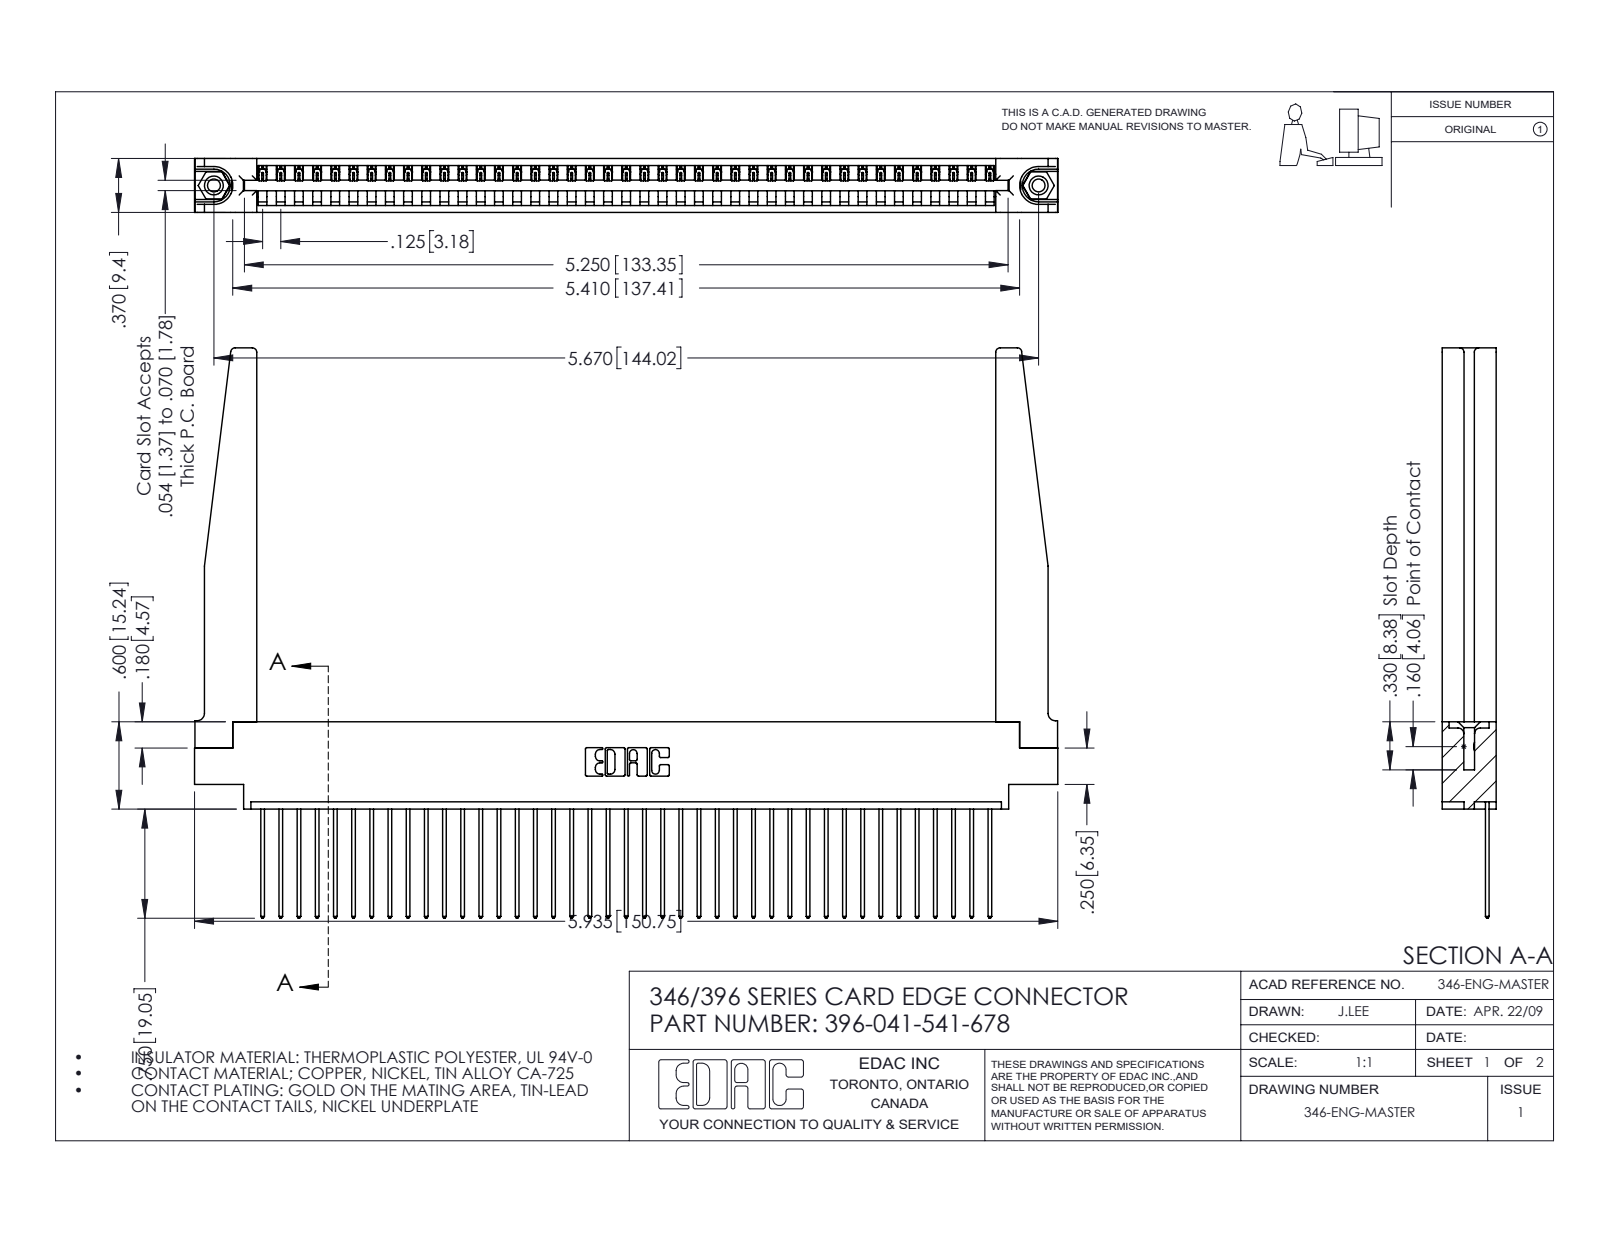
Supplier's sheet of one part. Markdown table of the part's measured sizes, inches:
| quantity | value |
| --- | --- |
| part name | 345-250-001_345-250-001-102; 346-220-078_345-220-078; 396-041-541-678; 346 Part_0.170 Offset - 0.156 Dia-TH (+1 more) |
| STEP written by | SolidWorks 2016 (CONFIG_CONTROL_DESIGN) |
| units | inches |
| bodies | 46 solids, 2738 faces (1862 planar, 824 cylindrical, 52 other) |
| overall size | 5.935 × 3.92 × 0.37 |
| volume | 1.301 in³ |
| surface area | 39.53 in² |
| round holes (diameter × count) | 0.089 × 2, 0.125 × 2, 0.156 × 2, 0.064 × 1 |
| round bosses / shafts (diameter × count) | 0.155 × 2 |
| partial cylindrical surfaces (radius × count) | 0.006 × 82, 0.01 × 82, 0.01 × 22, 0.03 × 8, 0.007 × 6, 0.031 × 6, 0.026 × 3, 0.031 × 2 |
| main face-to-face distances | 0.37, 0.048, 0.322, 0.072, 0.148, 0.25, 0.298, 0.025, 0.15, 0.222 |
| hole center spacings | 0.246, 5.461, 5.67 |
